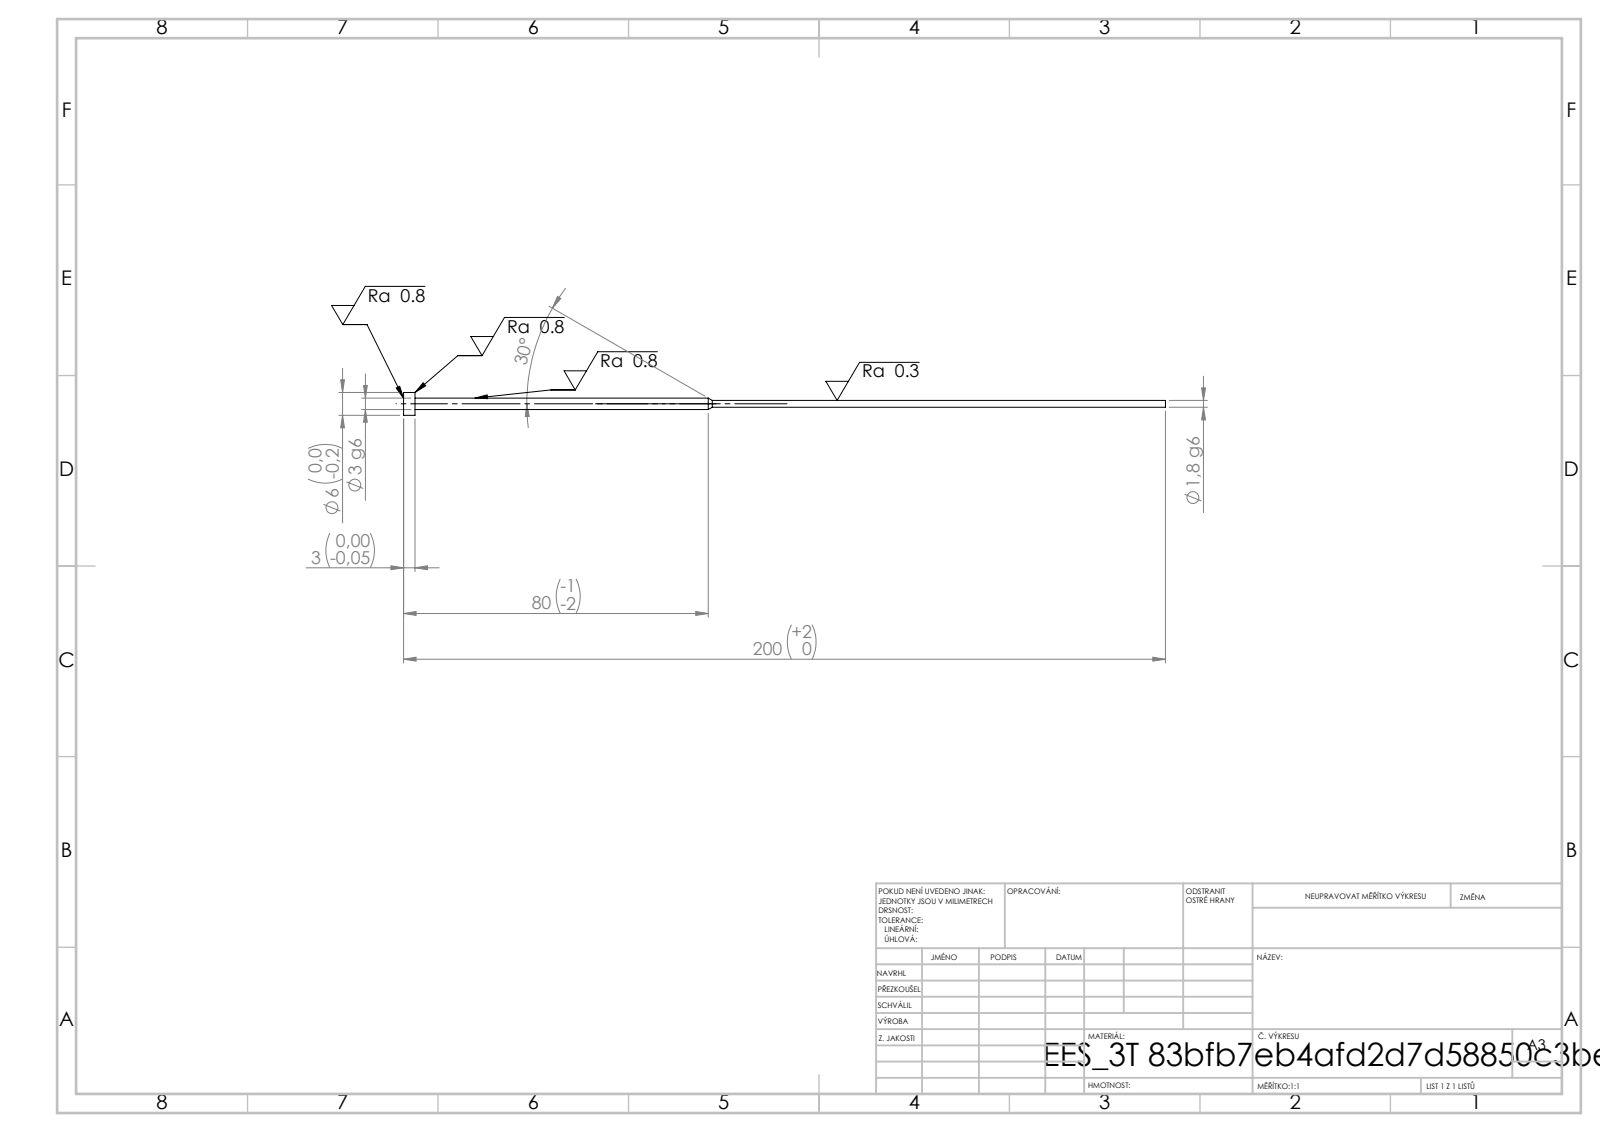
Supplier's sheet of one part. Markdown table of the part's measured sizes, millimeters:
| quantity | value |
| --- | --- |
| STEP written by | SolidWorks 2019 (CONFIG_CONTROL_DESIGN) |
| units | millimeters |
| bodies | 1 solid, 11 faces (3 planar, 6 cylindrical, 2 other) |
| overall size | 200 × 6 × 6 |
| volume | 937 mm³ |
| surface area | 1 516 mm² |
| round bosses / shafts (diameter × count) | 6 × 1, 3 × 1, 1.8 × 1 |
| main face-to-face distances | 3, 197, 200 |
